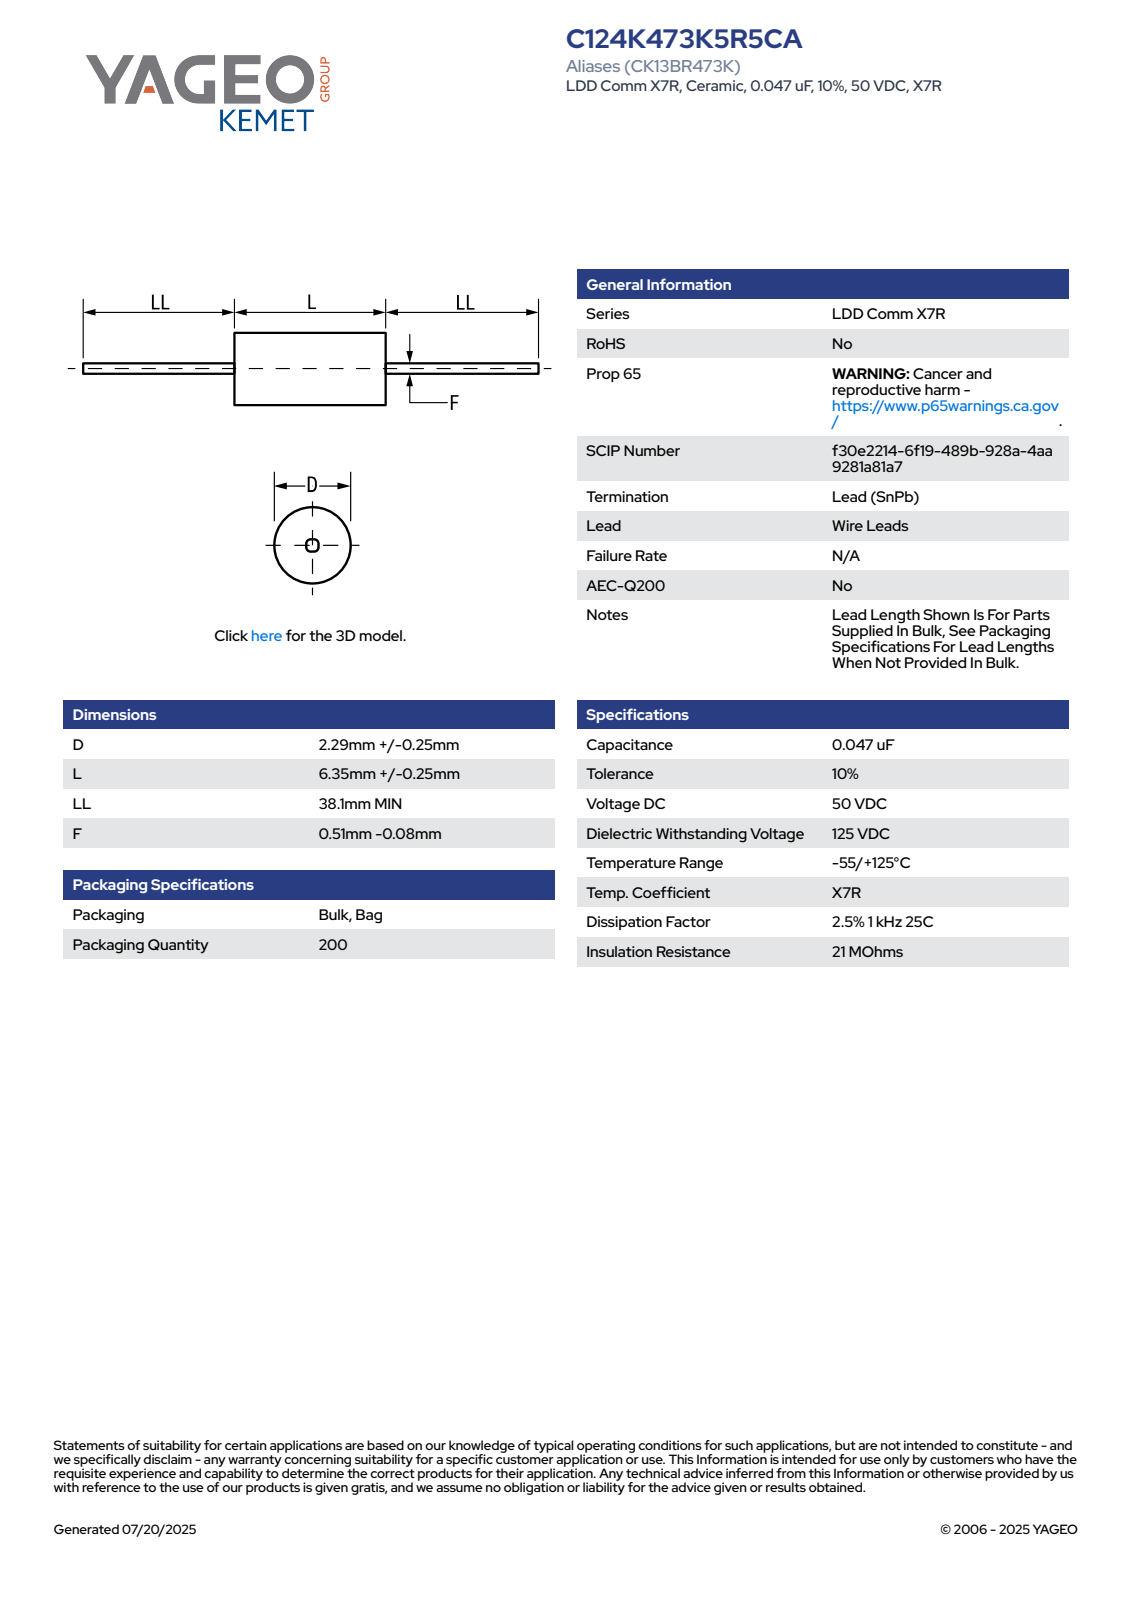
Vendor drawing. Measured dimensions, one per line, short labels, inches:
name: CCA_AXM_C124_D2.54L6.6LL38.1F0.43
written by: SolidWorks 2014 (AUTOMOTIVE_DESIGN)
unit: in
bodies: 1 solid, 66 faces (26 planar, 9 cylindrical, 31 other)
size: 3.26 × 0.1 × 0.1
volume: 0.003 in³; area: 0.257 in²
bosses: 1× ⌀0.1, 1× ⌀0.017
rounds: 1× R0.05
face distances: 0.26, 1.5, 1.76, 3.26
